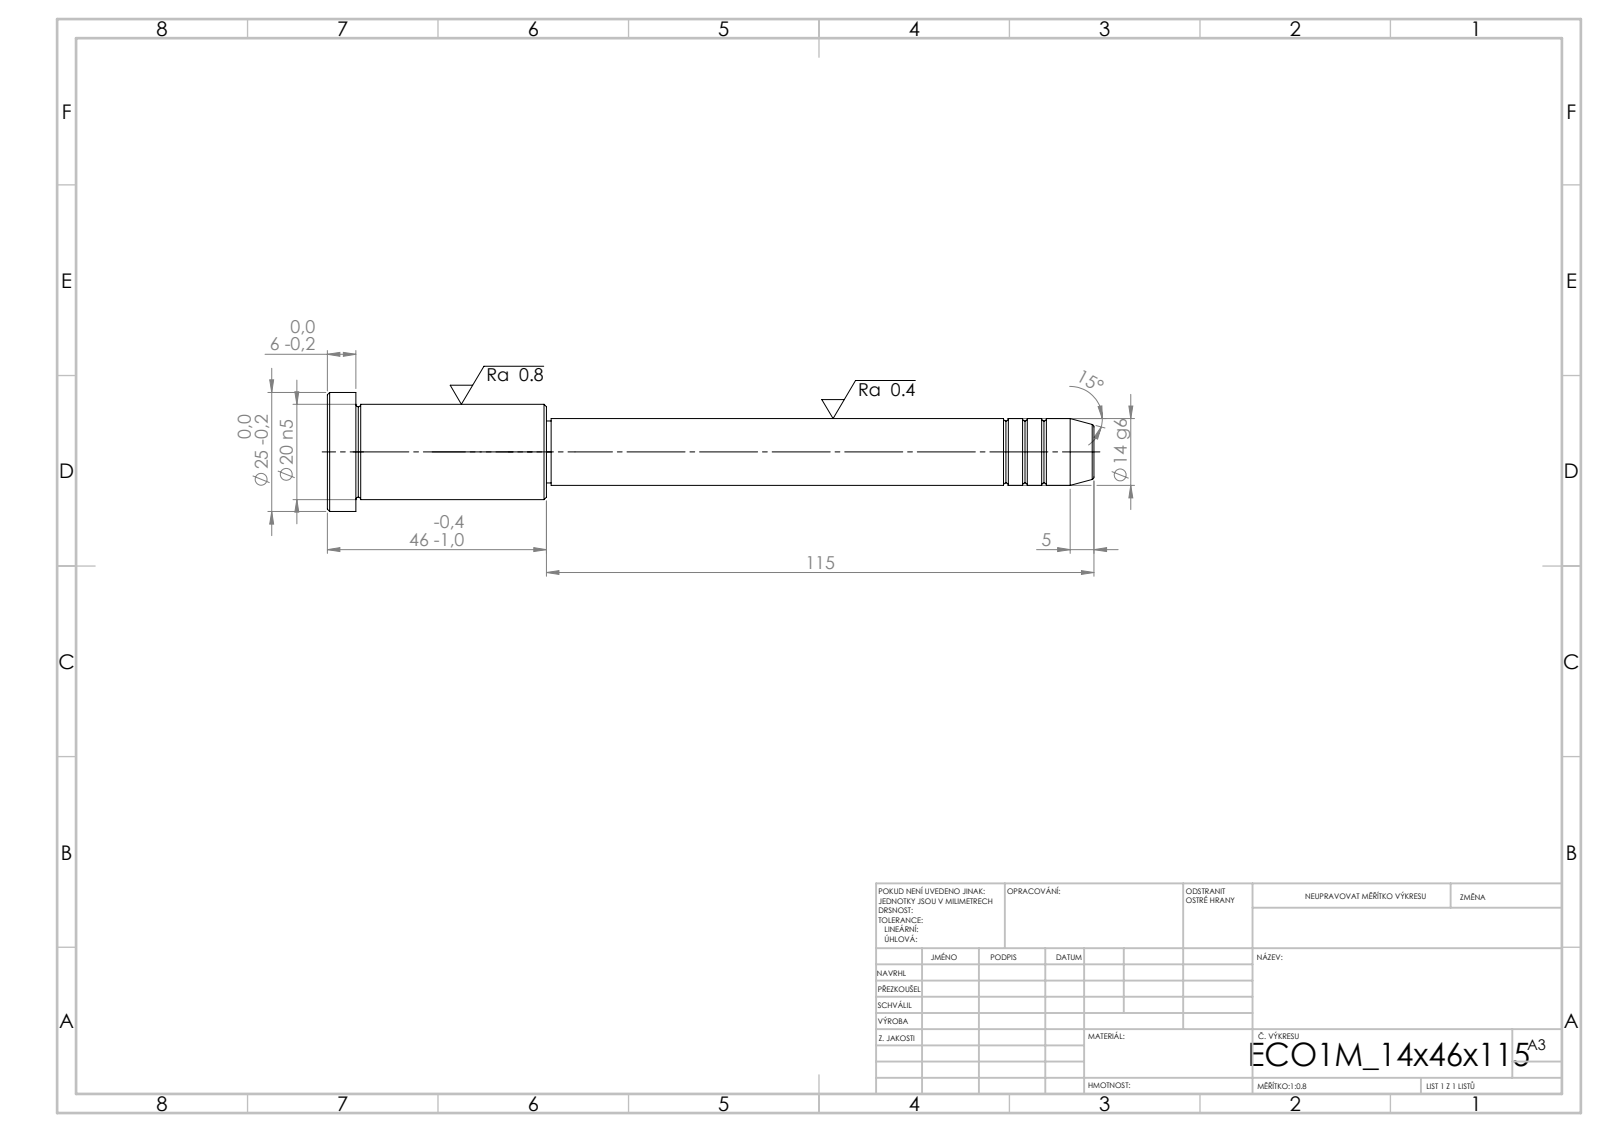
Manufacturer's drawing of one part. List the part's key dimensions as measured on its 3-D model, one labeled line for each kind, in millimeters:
STEP written by: SolidWorks 2019 (CONFIG_CONTROL_DESIGN)
Units: millimetres
Bodies: 1 solid, 43 faces (5 planar, 14 cylindrical, 24 other)
Overall size (bounding box): 161 × 25 × 25
Volume: 32 963 mm³ · Surface area: 9 049 mm²
Round bosses / shafts (diameter × count): ⌀25 ×1, ⌀20 ×1, ⌀14 ×1, ⌀13 ×1
Main face-to-face distances: 6, 40, 46, 115, 155, 161, 114, 1, 41, 47
